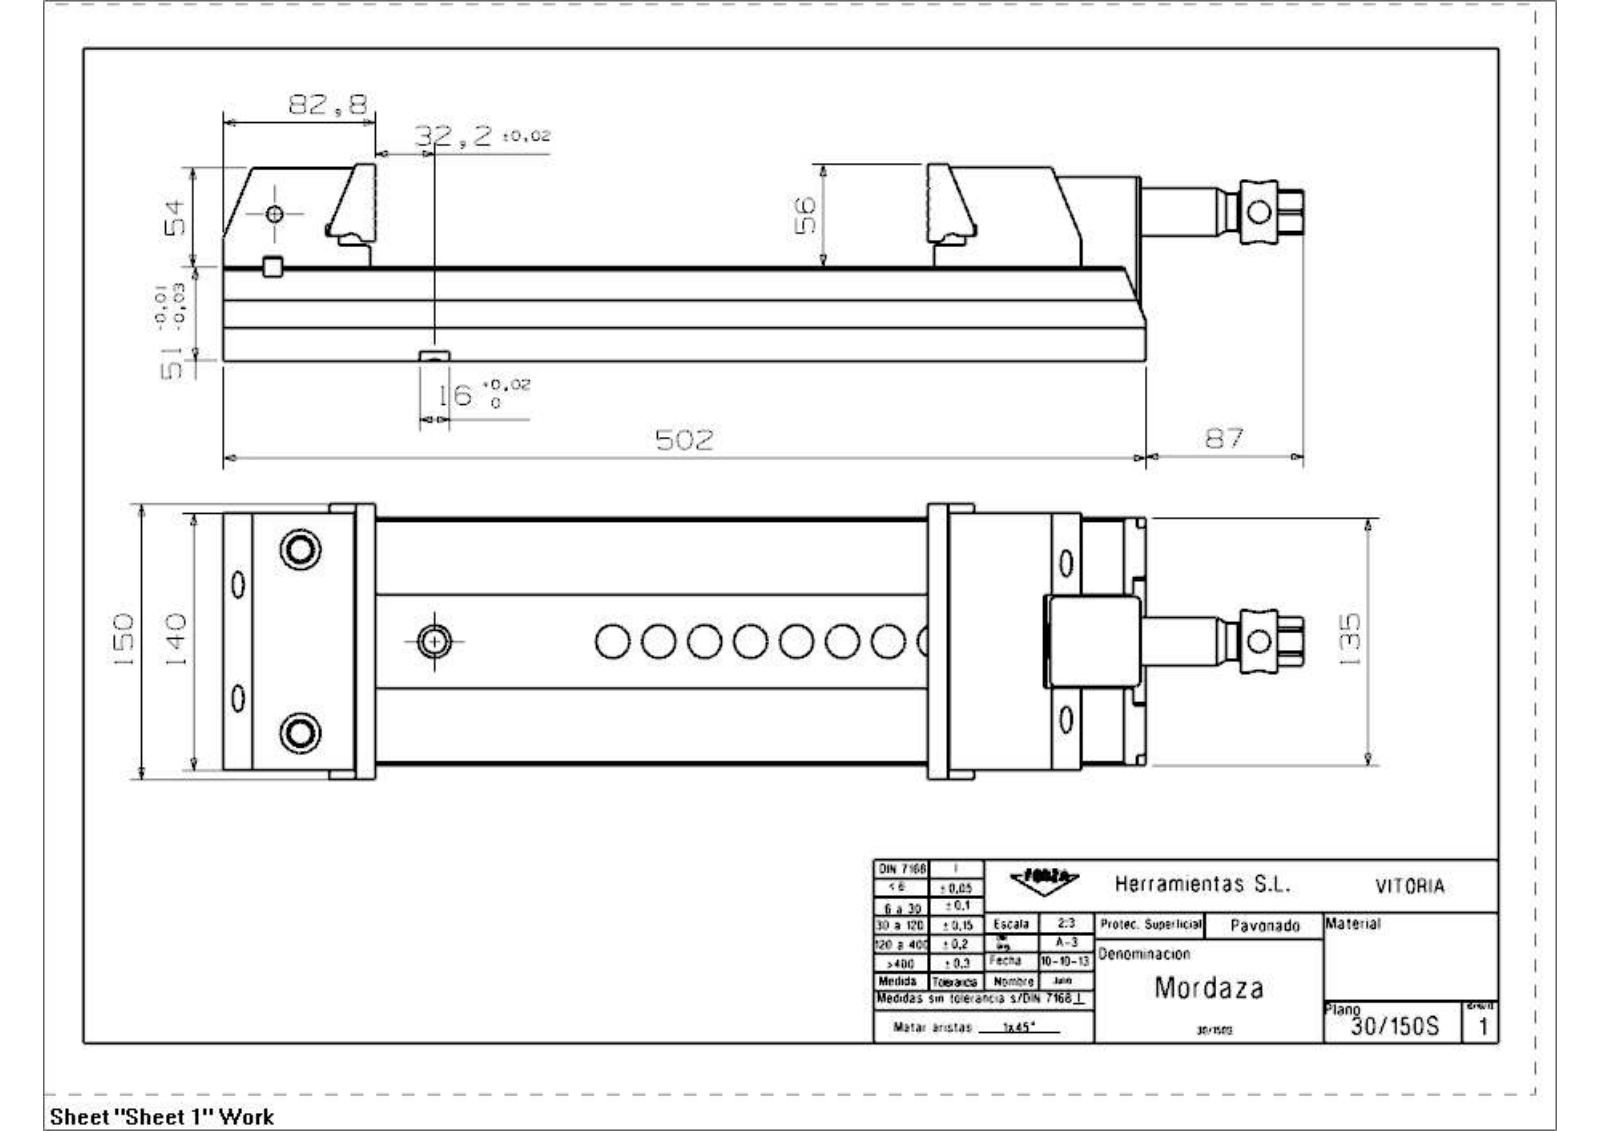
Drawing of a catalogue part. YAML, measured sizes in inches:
part_name: "30_150S_Mordaza"
step_written_by: "SIEMENS PLM Software NX 7.5 (CONFIG_CONTROL_DESIGN)"
units: inches
bodies: {solids: 12, faces: 450, planar: 296, cylindrical: 98, other: 56}
overall_size: [23.14, 5.906, 4.213]
volume: 222.2
surface_area: 773.5
round_holes:
  - {diameter: 0.512, count: 6}
  - {diameter: 0.591, count: 6}
  - {diameter: 0.204, count: 5}
  - {diameter: 0.275, count: 4}
  - {diameter: 0.335, count: 4}
  - {diameter: 0.346, count: 4}
  - {diameter: 0.417, count: 4}
  - {diameter: 0.748, count: 4}
  - {diameter: 0.382, count: 2}
  - {diameter: 0.394, count: 2}
  - {diameter: 0.472, count: 2}
  - {diameter: 0.487, count: 2}
round_bosses_or_shafts:
  - {diameter: 1.339, count: 1}
  - {diameter: 1.331, count: 1}
  - {diameter: 1.024, count: 1}
  - {diameter: 0.787, count: 1}
  - {diameter: 0.65, count: 1}
partial_cylinders:
  - {radius: 0.059, count: 4}
  - {radius: 0.315, count: 4}
  - {radius: 0.787, count: 4}
  - {radius: 0.063, count: 2}
  - {radius: 0.217, count: 2}
  - {radius: 0.236, count: 2}
  - {radius: 0.157, count: 1}
  - {radius: 0.354, count: 1}
face_to_face_distances: [2.008, 0.76, 1.248, 0.217, 4.134, 1.945, 0.063, 0.697, 5.315, 0.315]
hole_center_spacings: [0.453, 2.648, 2.894, 3.346, 3.747, 3.747, 0.454, 0.457]
